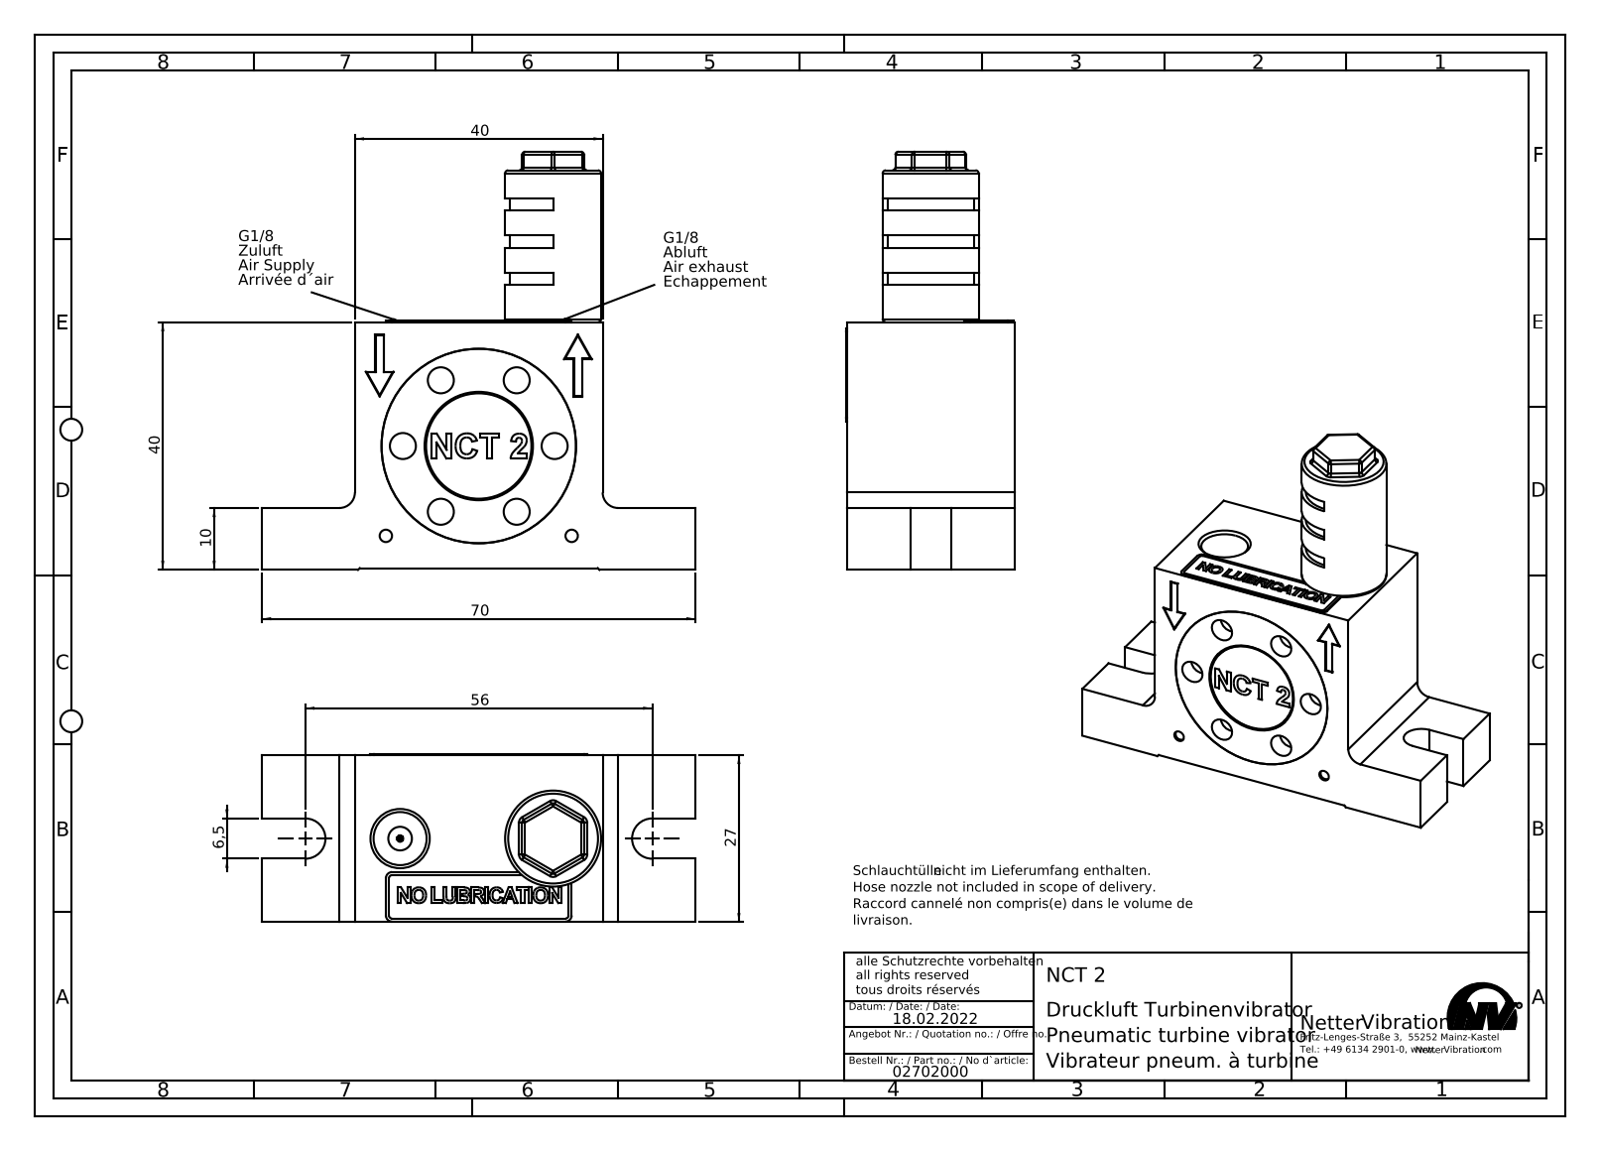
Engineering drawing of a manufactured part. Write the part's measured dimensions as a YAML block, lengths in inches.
part_name: "NCT 2 Turbinenvibrator #02702000"
step_written_by: "SolidWorks 2015 (AUTOMOTIVE_DESIGN)"
units: inches
bodies: {solids: 6, faces: 388, planar: 242, cylindrical: 79, other: 67}
overall_size: [2.756, 2.657, 1.081]
volume: 3.356
surface_area: 27.45
round_holes:
  - {diameter: 0.165, count: 6}
  - {diameter: 0.079, count: 2}
  - {diameter: 0.337, count: 2}
  - {diameter: 0.551, count: 1}
  - {diameter: 0.689, count: 1}
  - {diameter: 0.748, count: 1}
  - {diameter: 1.161, count: 1}
round_bosses_or_shafts:
  - {diameter: 1.26, count: 1}
  - {diameter: 1.16, count: 1}
  - {diameter: 1.074, count: 1}
  - {diameter: 0.669, count: 1}
  - {diameter: 0.61, count: 1}
  - {diameter: 0.383, count: 1}
partial_cylinders:
  - {radius: 0.02, count: 22}
  - {radius: 0.039, count: 4}
  - {radius: 0.098, count: 2}
  - {radius: 0.128, count: 2}
  - {radius: 0.276, count: 1}
face_to_face_distances: [1.575, 1.063, 1.563, 0.157, 0.906, 1.069, 0.394, 1.181, 0.382, 0.913]
hole_center_spacings: [0.482, 0.835, 0.965, 0.381, 0.482, 0.581, 0.821, 0.835]
